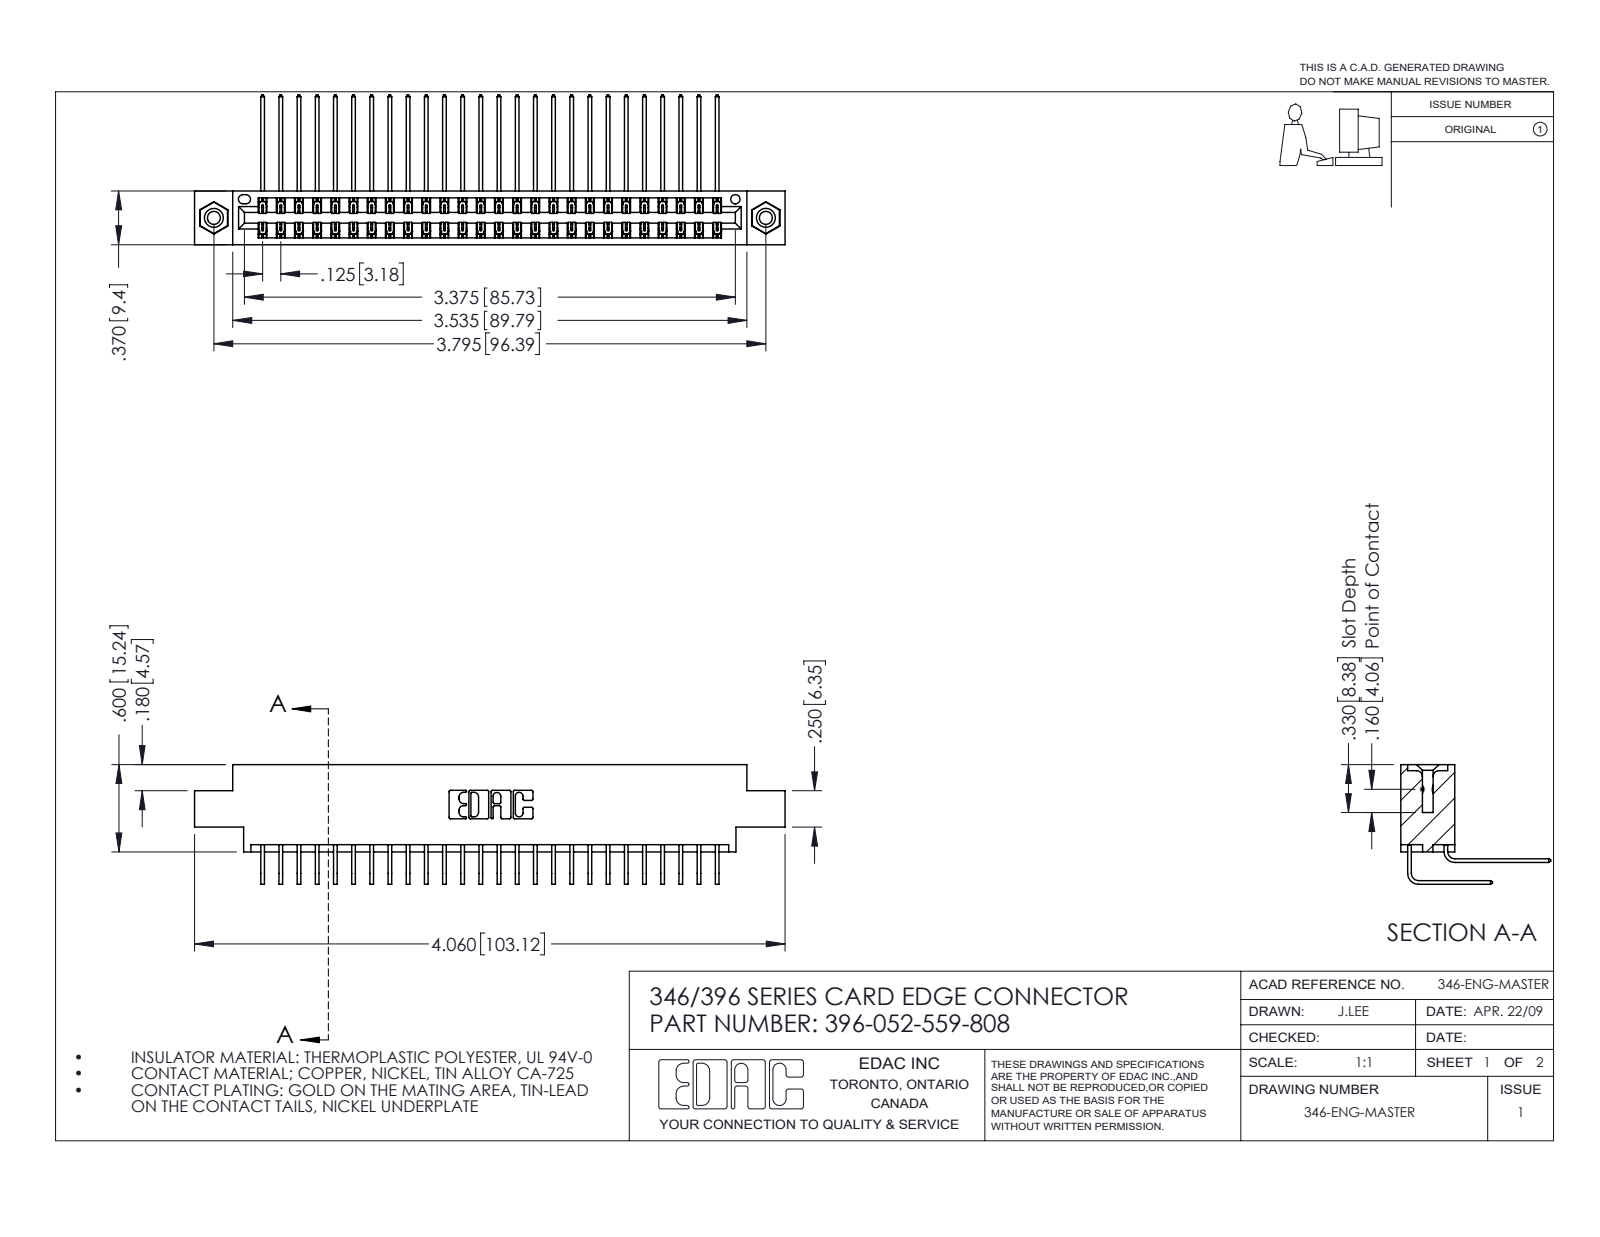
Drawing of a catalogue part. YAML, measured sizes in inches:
part_name: "345-250-001_345-250-003-102; 345-292-001_559 Tail - 2; 396-052-559-808; 346 Part_0.170 Offset - 0.156 Dia-TI (+1 more)"
step_written_by: "SolidWorks 2016 (CONFIG_CONTROL_DESIGN)"
units: inches
bodies: {solids: 55, faces: 2994, planar: 2036, cylindrical: 942, other: 16}
overall_size: [4.06, 1.03, 0.823]
volume: 0.615
surface_area: 23.61
round_holes:
  - {diameter: 0.089, count: 2}
  - {diameter: 0.125, count: 2}
  - {diameter: 0.156, count: 2}
  - {diameter: 0.064, count: 1}
round_bosses_or_shafts:
  - {diameter: 0.155, count: 2}
partial_cylinders:
  - {radius: 0.006, count: 78}
  - {radius: 0.01, count: 22}
  - {radius: 0.007, count: 6}
  - {radius: 0.031, count: 6}
  - {radius: 0.026, count: 3}
  - {radius: 0.014, count: 2}
  - {radius: 0.022, count: 2}
  - {radius: 0.024, count: 2}
face_to_face_distances: [0.048, 0.322, 0.025, 0.37, 0.25, 0.072, 0.298, 0.275, 0.222, 0.148]
hole_center_spacings: [0.246, 3.587, 3.795]
